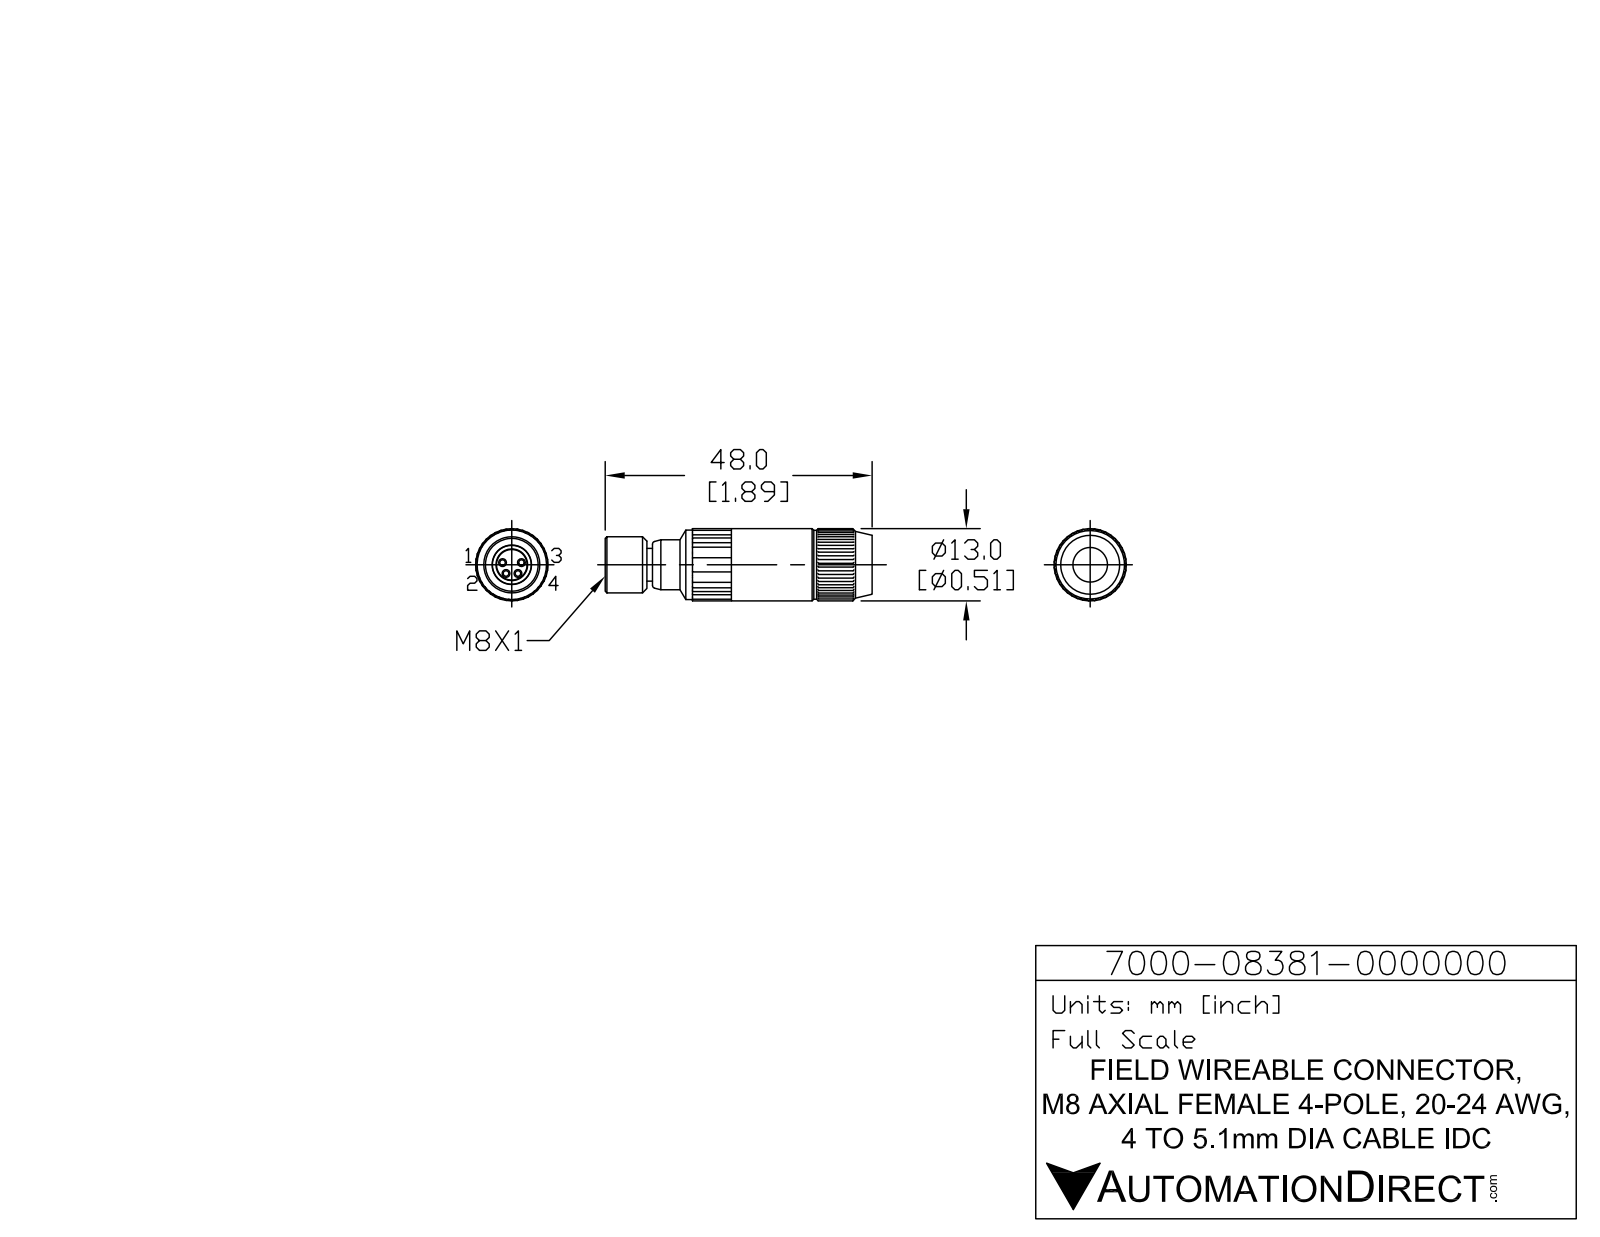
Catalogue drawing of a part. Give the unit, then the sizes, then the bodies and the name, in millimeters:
Units: millimetres
Overall size (bounding box): 48 × 13 × 13
Round holes (diameter × count): ⌀1 ×4, ⌀5.84 ×1, ⌀8.08 ×1
Round bosses / shafts (diameter × count): ⌀13 ×1, ⌀12.39 ×1, ⌀12.13 ×1, ⌀11.99 ×1, ⌀9 ×1, ⌀6.8 ×1, ⌀5.8 ×1
Partial cylindrical surfaces — rounded edges, fillets, slot ends (radius × count): R5.1 ×1
Main face-to-face distances: 4.68, 48, 40.5, 7.5, 10, 38, 30.5, 24.61, 14.61, 15.89
Hole centre spacings: 1.5, 1.66, 1.7, 2.66, 1.4, 3
Volume: 4 831 mm³ · Surface area: 2 822 mm²
Bodies: 1 solid, 681 faces (423 planar, 172 cylindrical, 86 other)
Part name (STEP PRODUCT): 7000-08381-0000000
STEP written by: SolidWorks 2015 (AUTOMOTIVE_DESIGN)
